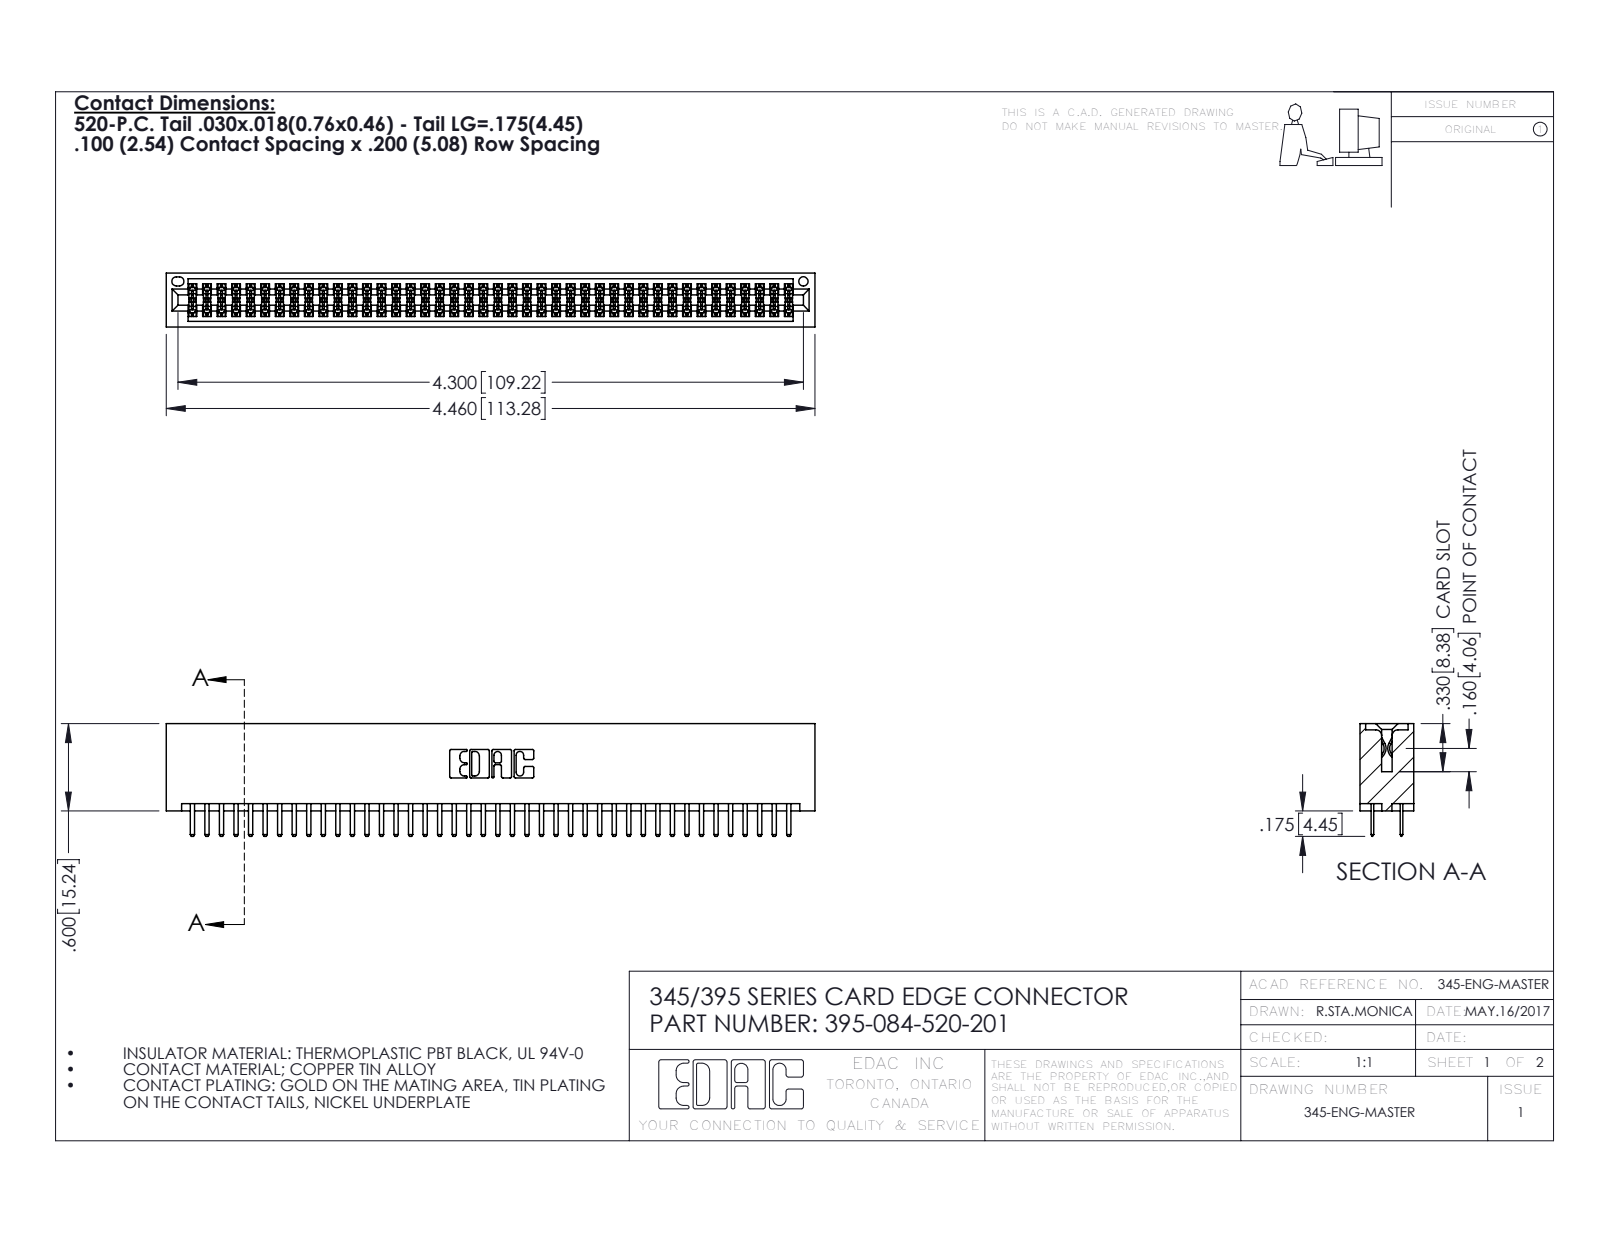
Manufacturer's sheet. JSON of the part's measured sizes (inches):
{"part_name": "345 Part_No Mounting Lugs; 395-084-520-201; 345-292-001_345-293-120", "step_written_by": "SolidWorks 2016 (CONFIG_CONTROL_DESIGN)", "units": "inches", "bodies": {"solids": 85, "faces": 4654, "planar": 3016, "cylindrical": 1638, "other": 0}, "overall_size": [4.46, 0.775, 0.37], "volume_in3": 0.707, "surface_area_in2": 26.89, "round_holes": [[0.064, 1]], "partial_cylinders_radius": [[0.006, 126], [0.01, 88], [0.01, 22], [0.007, 6], [0.031, 6], [0.026, 3], [0.014, 2], [0.019, 2]], "face_to_face_distances": [0.298, 0.072, 0.2, 0.37, 0.098, 0.272, 0.025, 0.225, 0.022, 0.072]}
